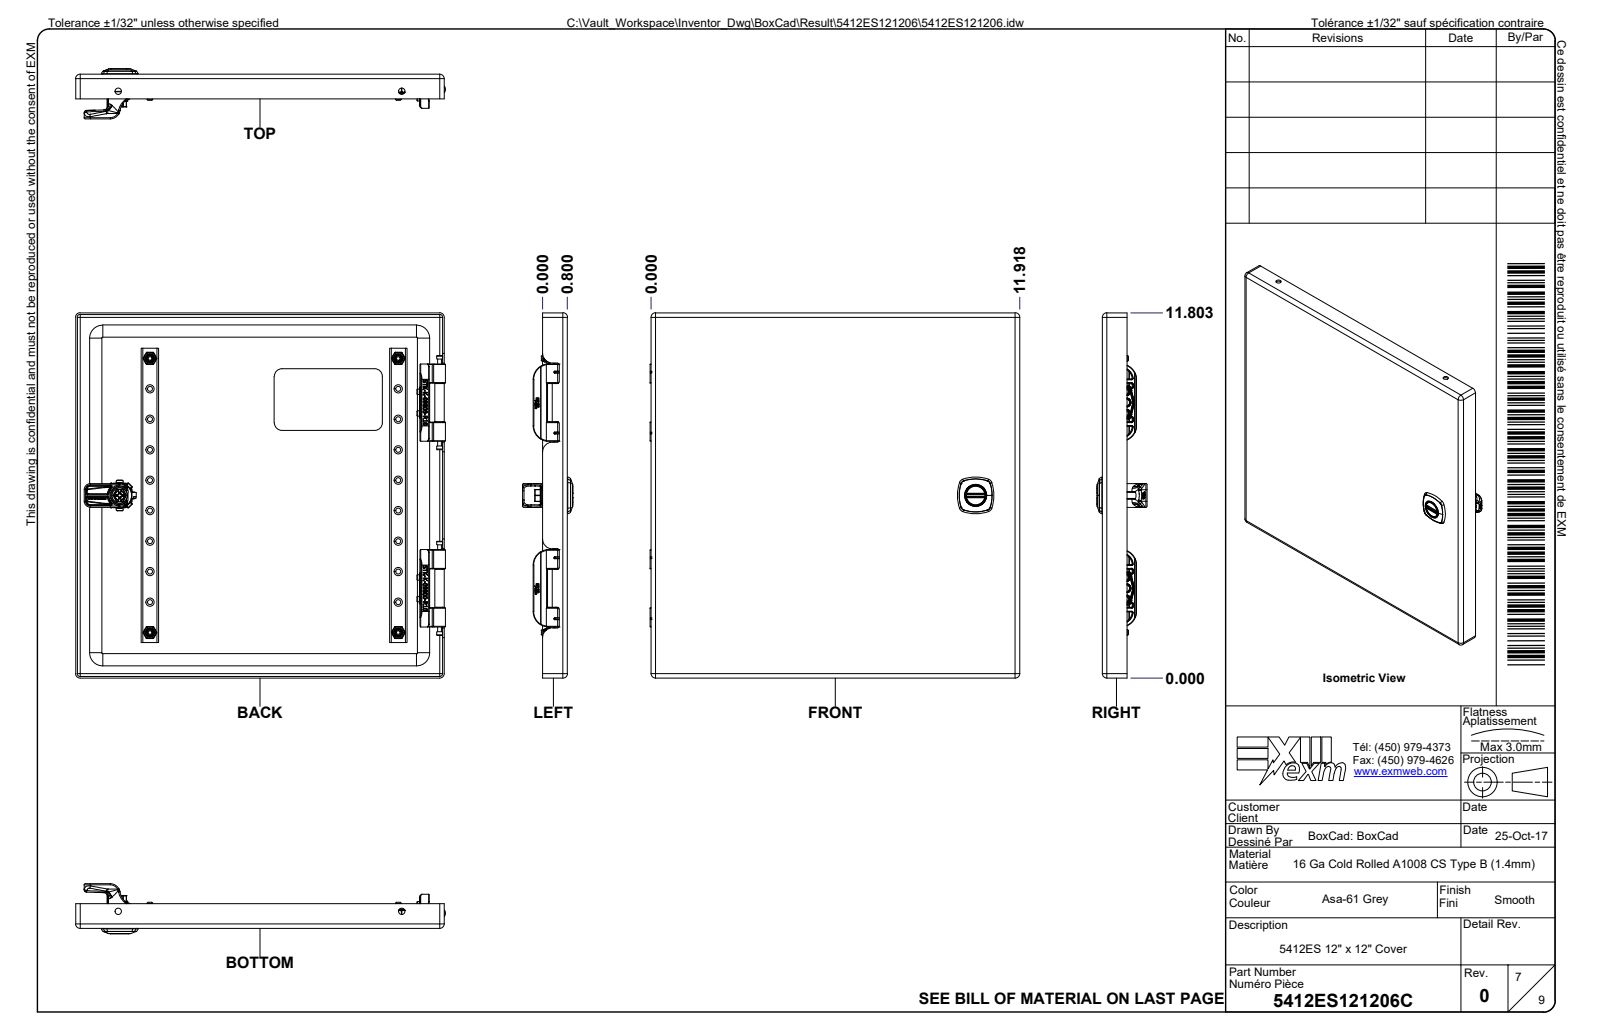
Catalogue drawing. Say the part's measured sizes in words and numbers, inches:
The part is named "5412ES121206; 5412ES121206B; 5412ES121206B-P; STK-Q-16005 (+8 more)". Its 3-D file was written by "Autodesk Inventor 2024 (AUTOMOTIVE_DESIGN)". It is 56 solids with 8355 faces: 2237 planar, 2205 cylindrical and 3913 other. Overall it measures 12.003 by 12 by 7.31 inches. Its volume is 53.66 cubic inches and its surface area 1 754 square inches. Round holes: 16 of diameter 0.165, 9 of diameter 0.03, 8 of diameter 0.043, 8 of diameter 0.315, 7 of diameter 0.201, 5 of diameter 0.311, 4 of diameter 0.178, 4 of diameter 0.197, 4 of diameter 0.268, 4 of diameter 0.27, 4 of diameter 0.29, 4 of diameter 0.39. Round bosses or shafts: 16 of diameter 0.237, 9 of diameter 0.03, 8 of diameter 0.232, 8 of diameter 0.039, 4 of diameter 0.717, 4 of diameter 0.374, 4 of diameter 0.311, 4 of diameter 0.262. Partial cylindrical surfaces (rounded edges, fillets, slot ends): 189 of radius 0.02, 107 of radius 0.01, 93 of radius 0.039, 78 of radius 0.008, 30 of radius 0.016, 26 of radius 0.012, 24 of radius 0.031, 24 of radius 0.084. The main face-to-face distances are 0.053, 11.947, 7.081, 7.028, 12, 11.894, 7.135, 0.927, 0.874, 6.154. The hole center spacings are 1.969, 0.984, 8.091, 8.269, 2.953, 8.557, 3.937, 8.944.
